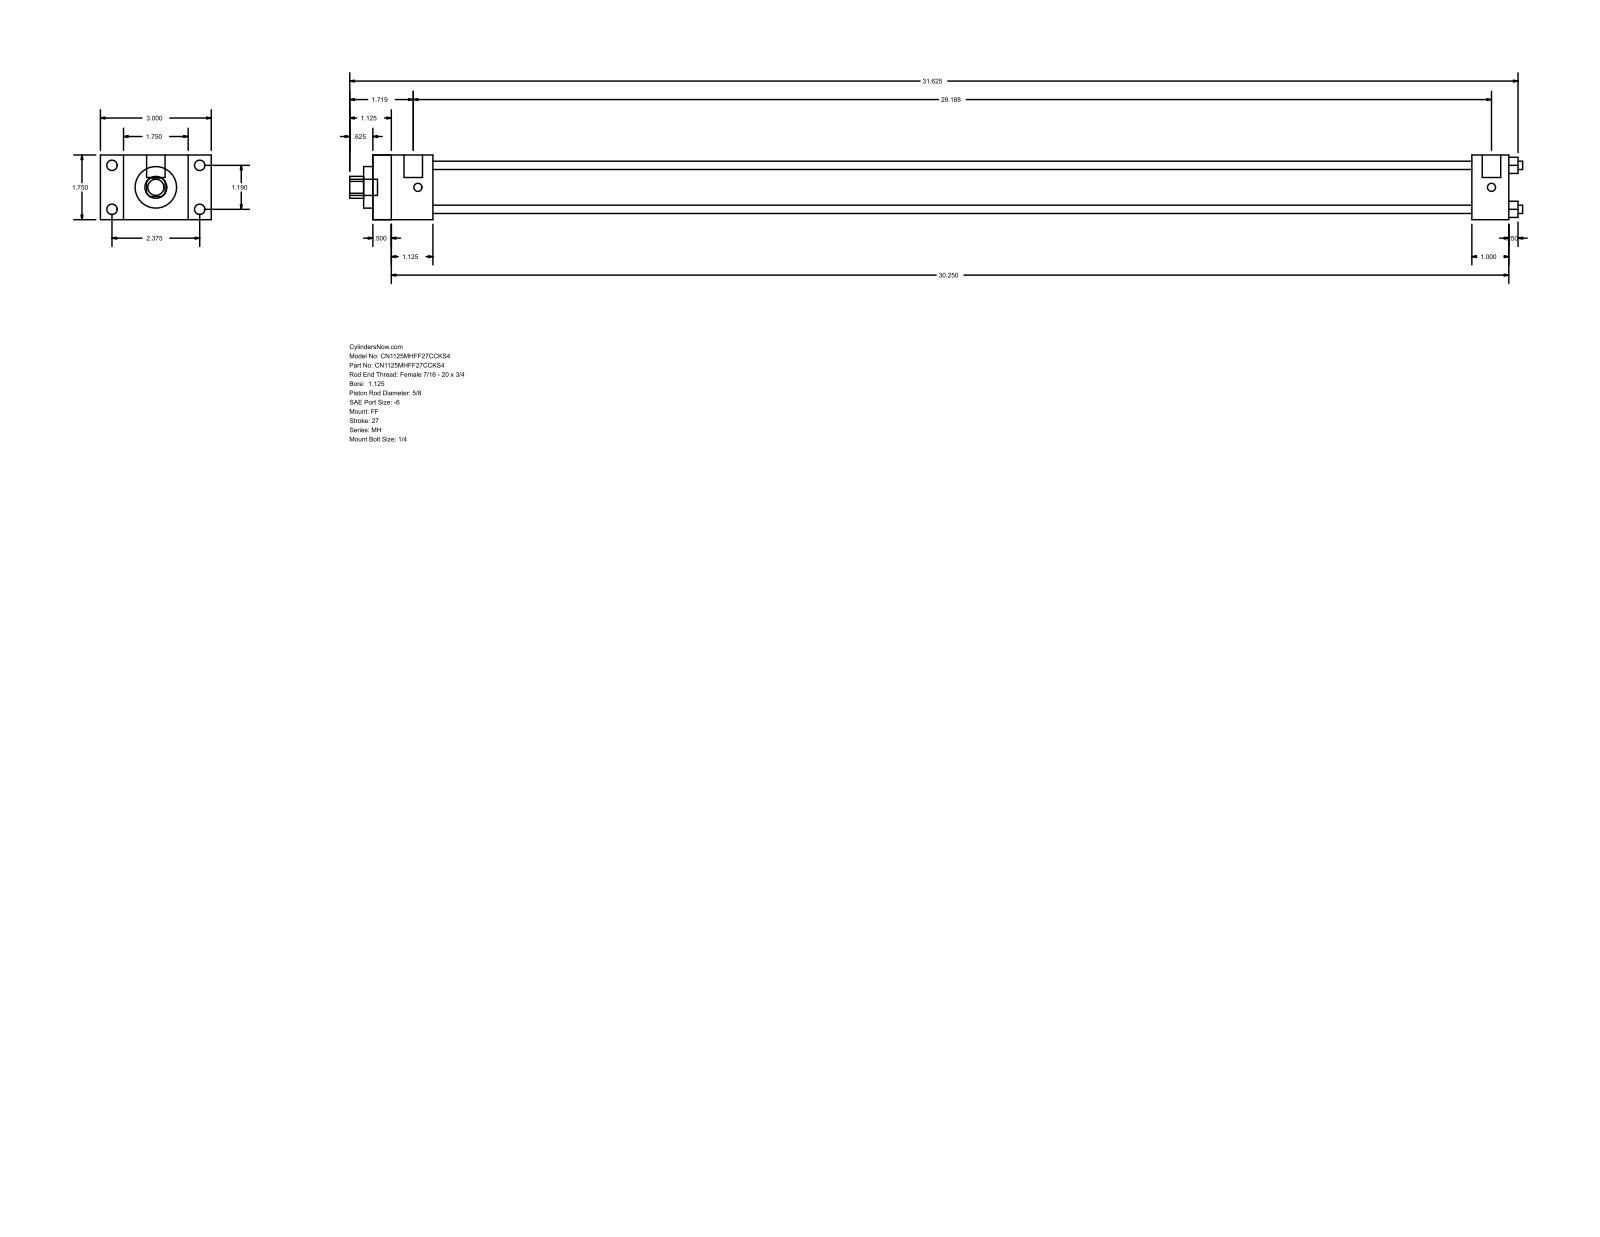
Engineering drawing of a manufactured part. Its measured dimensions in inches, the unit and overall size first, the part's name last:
Units: inches
Overall size (bounding box): 31.75 × 3 × 1.75
Round holes (diameter × count): ⌀0.225 ×4, ⌀0.625 ×1, ⌀1.125 ×1, ⌀1.375 ×1
Round bosses / shafts (diameter × count): ⌀0.281 ×4, ⌀0.219 ×4, ⌀0.5 ×2, ⌀0.437 ×1
Partial cylindrical surfaces — rounded edges, fillets, slot ends (radius × count): R0.297 ×1
Main face-to-face distances: 1.75, 30.75, 0.5, 30.25, 0.625, 2.375, 1.125, 1.625, 29.75, 29.25
Hole centre spacings: 0.841, 1.19, 1.683
Bodies: 0 solids, 92 faces (64 planar, 28 cylindrical, 0 other)
Part name (STEP PRODUCT): MH_FF__0112_0.625
STEP written by: GSSL Pune (CONFIG_CONTROL_DESIGN)
